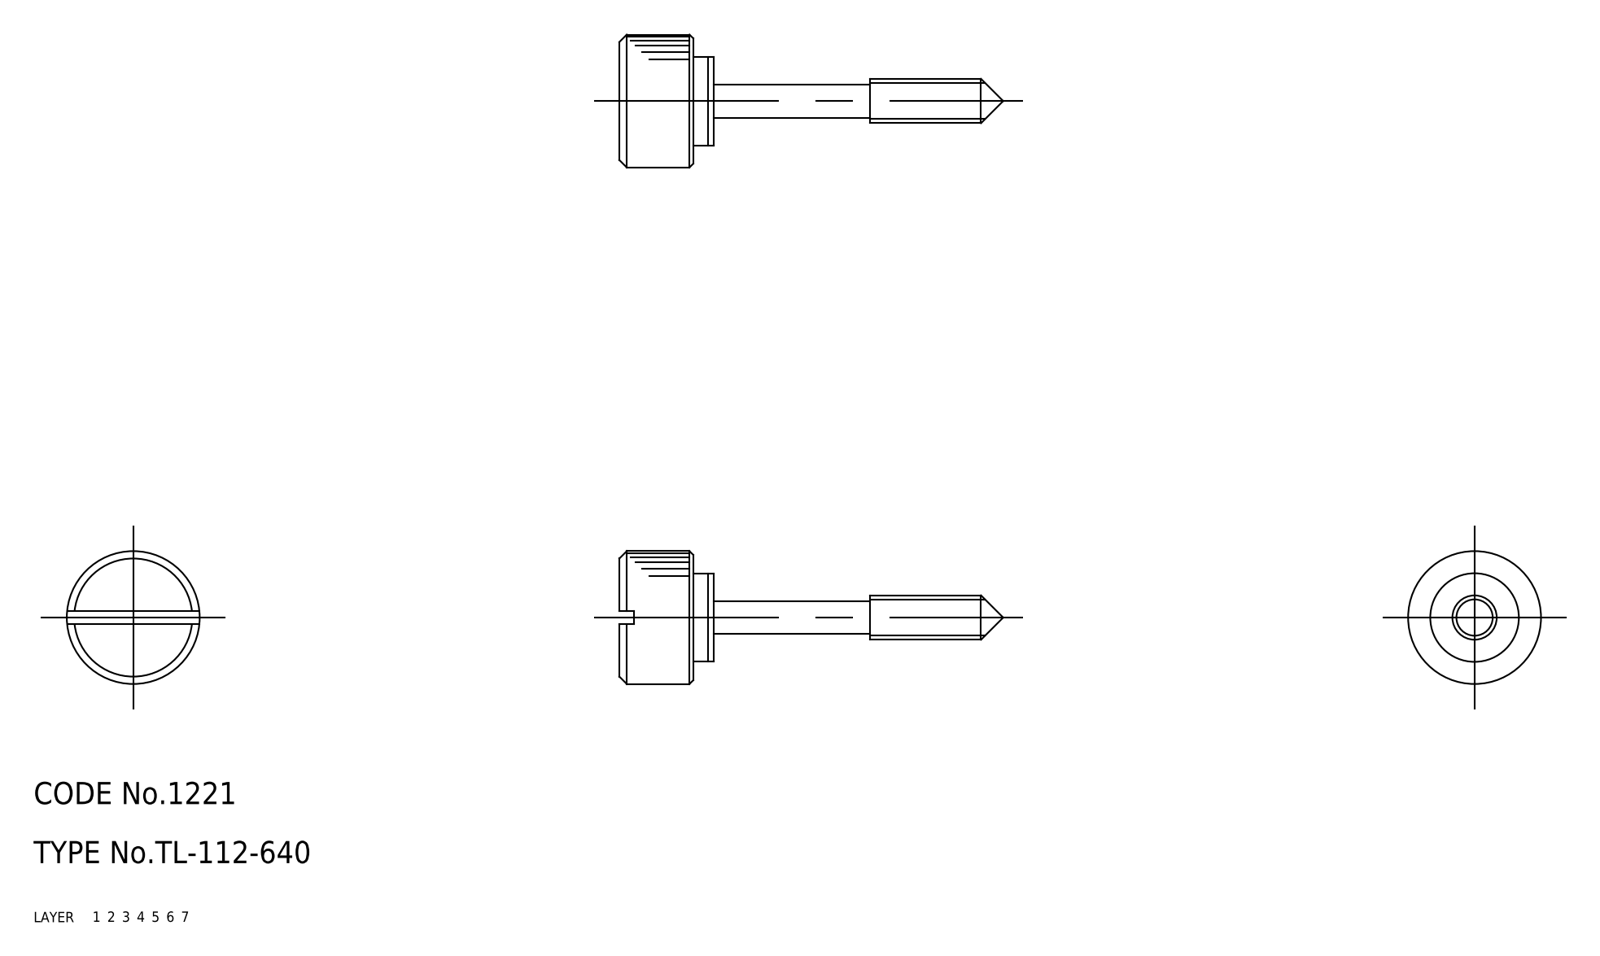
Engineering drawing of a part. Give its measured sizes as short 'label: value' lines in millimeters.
name: washer; knob; TL_112_640_9076_36
written by: CADfix (AUTOMOTIVE_DESIGN)
unit: mm
bodies: 2 solids, 42 faces (0 planar, 0 cylindrical, 42 other)
size: 52 × 18 × 18
volume: 3 553 mm³; area: 2 014 mm²
